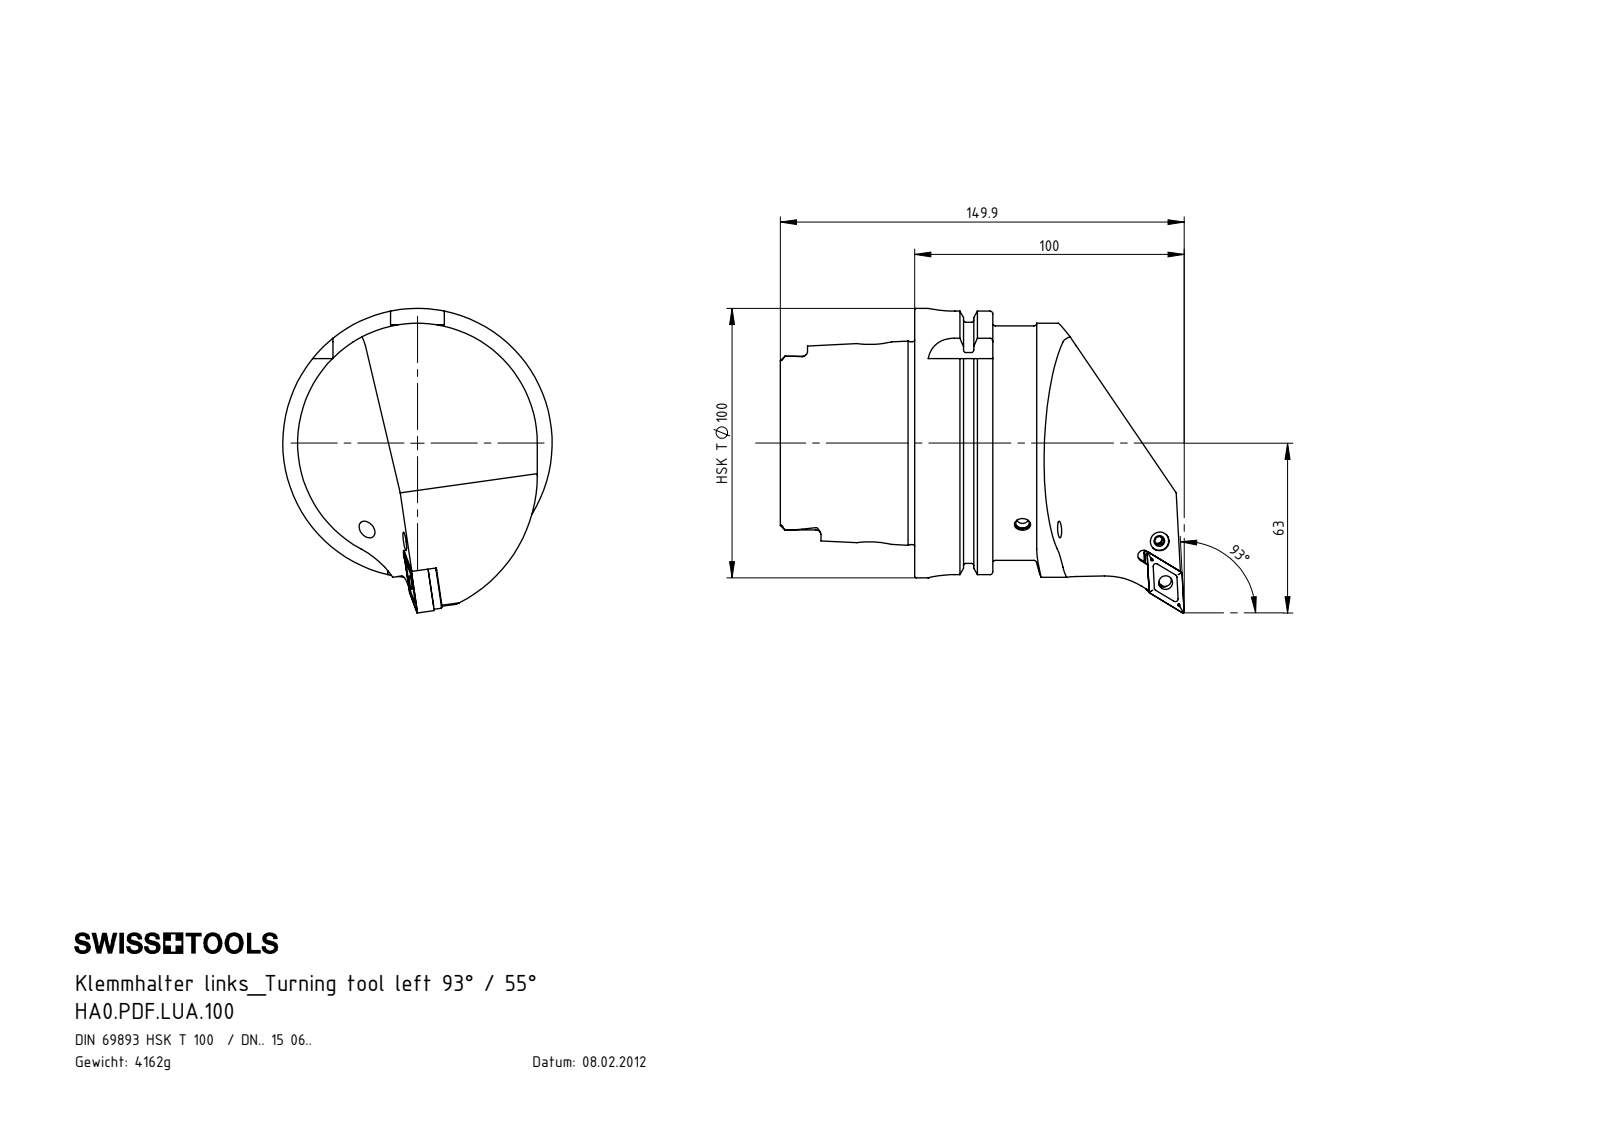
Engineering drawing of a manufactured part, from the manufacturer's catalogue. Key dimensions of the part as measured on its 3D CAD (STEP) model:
Part name (STEP PRODUCT): HA0-PDF.LUA.100; WCD-ER1.101.000; WDF-ER3.101.000_A; WCD-ER4.101.017_A (+4 more)
STEP written by: SolidWorks 2012 (CONFIG_CONTROL_DESIGN)
Units: millimetres
Bodies: 8 solids, 372 faces (115 planar, 103 cylindrical, 154 other)
Overall size (bounding box): 149.9 × 113.01 × 100
Volume: 531 148 mm³ · Surface area: 71 003 mm²
Round holes (diameter × count): ⌀5 ×3, ⌀12 ×2, ⌀5.16 ×1, ⌀6 ×1, ⌀6.4 ×1, ⌀7 ×1, ⌀8.4 ×1, ⌀10 ×1, ⌀22.5 ×1, ⌀26 ×1, ⌀53 ×1, ⌀63 ×1
Round bosses / shafts (diameter × count): ⌀100 ×1, ⌀91.95 ×1, ⌀87 ×1, ⌀75.26 ×1, ⌀8 ×1, ⌀7.9 ×1, ⌀6.4 ×1, ⌀6 ×1
Partial cylindrical surfaces — rounded edges, fillets, slot ends (radius × count): R1.9 ×6, R0.4 ×4, R1 ×4, R10 ×4, R2.5 ×2, R4.83 ×2, R4.88 ×2, R2.1 ×1
Main face-to-face distances: 12.45, 28.95, 16.5, 49.9, 62.35, 78.85, 87.8, 78.2, 28.3, 15.85
Hole centre spacings: 15.63
